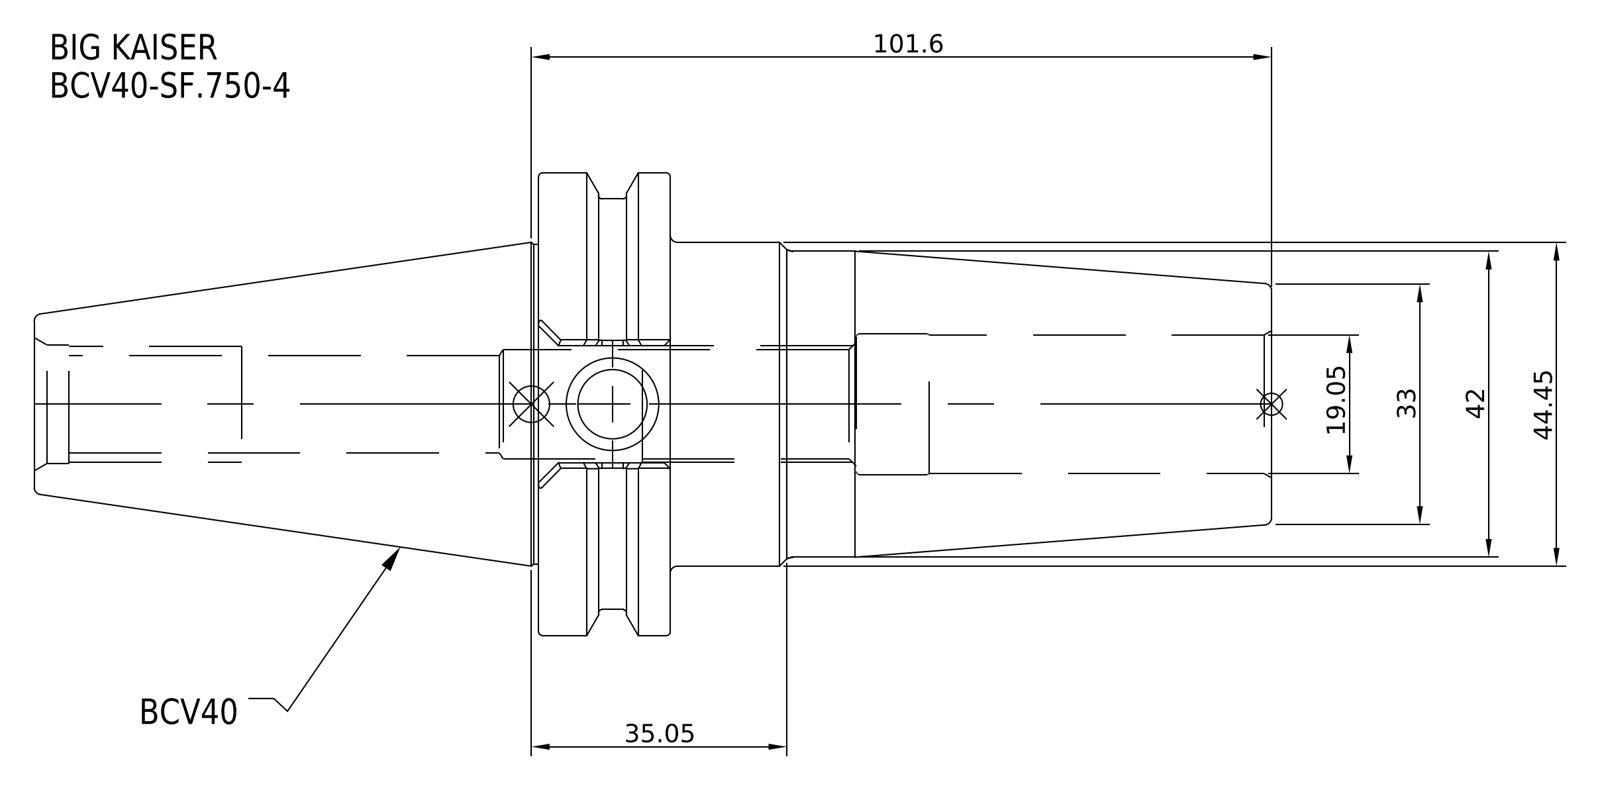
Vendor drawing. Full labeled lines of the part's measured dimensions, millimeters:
Part name (STEP PRODUCT): BCV40-SF_750-4
STEP written by: SolidWorks 2021 (CONFIG_CONTROL_DESIGN)
Units: millimetres
Bodies: 1 solid, 30 faces (8 planar, 14 cylindrical, 8 other)
Overall size (bounding box): 169.85 × 63.5 × 63.5
Volume: 208 699 mm³ · Surface area: 29 764 mm²
Round holes (diameter × count): ⌀19.05 ×1
Round bosses / shafts (diameter × count): ⌀63.5 ×1, ⌀56.36 ×1, ⌀44.45 ×1, ⌀42 ×1
Main face-to-face distances: 18.05, 82.55, 100.6, 169.85, 87.3, 69.25, 47, 35.55, 53.6, 122.85
